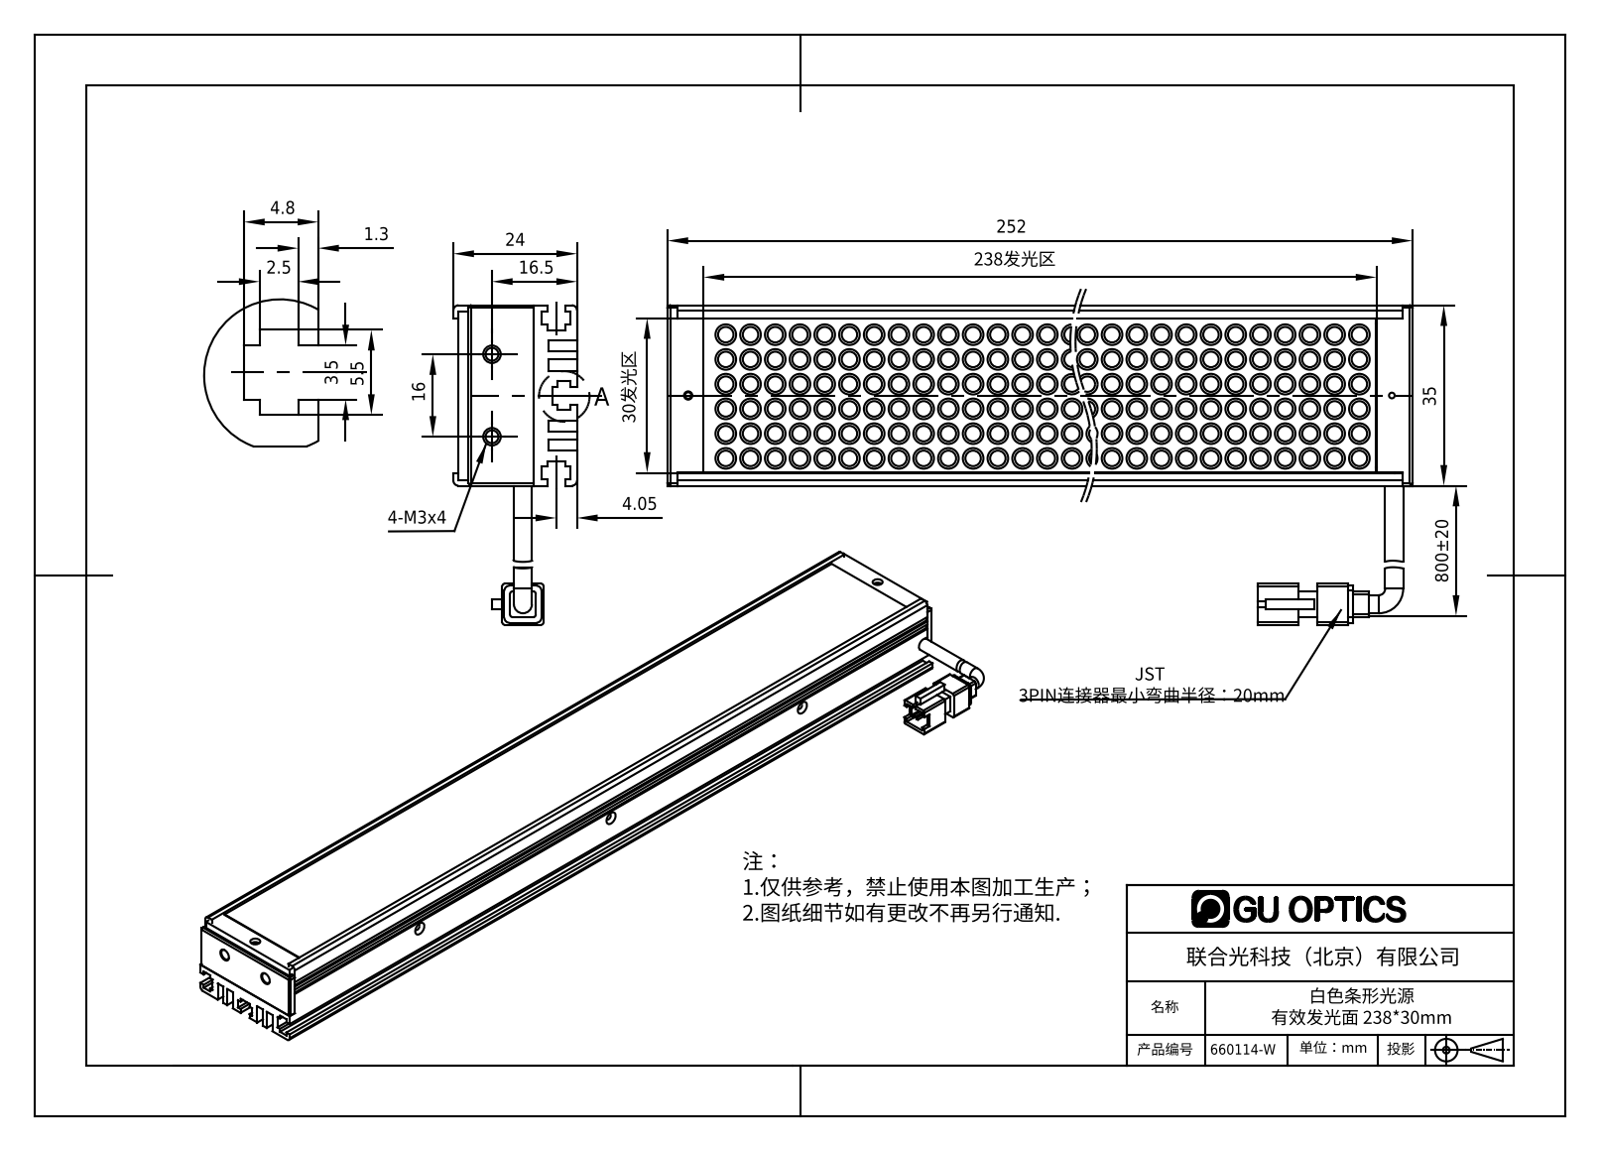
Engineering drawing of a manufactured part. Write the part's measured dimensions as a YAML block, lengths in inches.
part_name: "660114-W"
step_written_by: "SolidWorks 2016 (AUTOMOTIVE_DESIGN)"
units: inches
bodies: {solids: 8, faces: 2226, planar: 562, cylindrical: 1263, other: 401}
overall_size: [9.921, 2.441, 0.945]
volume: 6.821
surface_area: 198
round_holes:
  - {diameter: 0.063, count: 5}
  - {diameter: 0.067, count: 3}
  - {diameter: 0.059, count: 2}
  - {diameter: 0.098, count: 2}
  - {diameter: 0.11, count: 2}
  - {diameter: 0.118, count: 2}
  - {diameter: 0.043, count: 1}
  - {diameter: 0.049, count: 1}
  - {diameter: 0.079, count: 1}
round_bosses_or_shafts:
  - {diameter: 0.157, count: 294}
  - {diameter: 0.118, count: 294}
  - {diameter: 0.138, count: 2}
partial_cylinders:
  - {radius: 0.039, count: 12}
  - {radius: 0.02, count: 8}
  - {radius: 0.065, count: 1}
face_to_face_distances: [0.079, 0.087, 0.339, 0.039, 0.098, 0.354, 0.157, 0.496, 0.575, 0.417]
hole_center_spacings: [9.606, 0.276, 1.852, 1.863, 2.953, 4.804, 4.808, 7.756]
